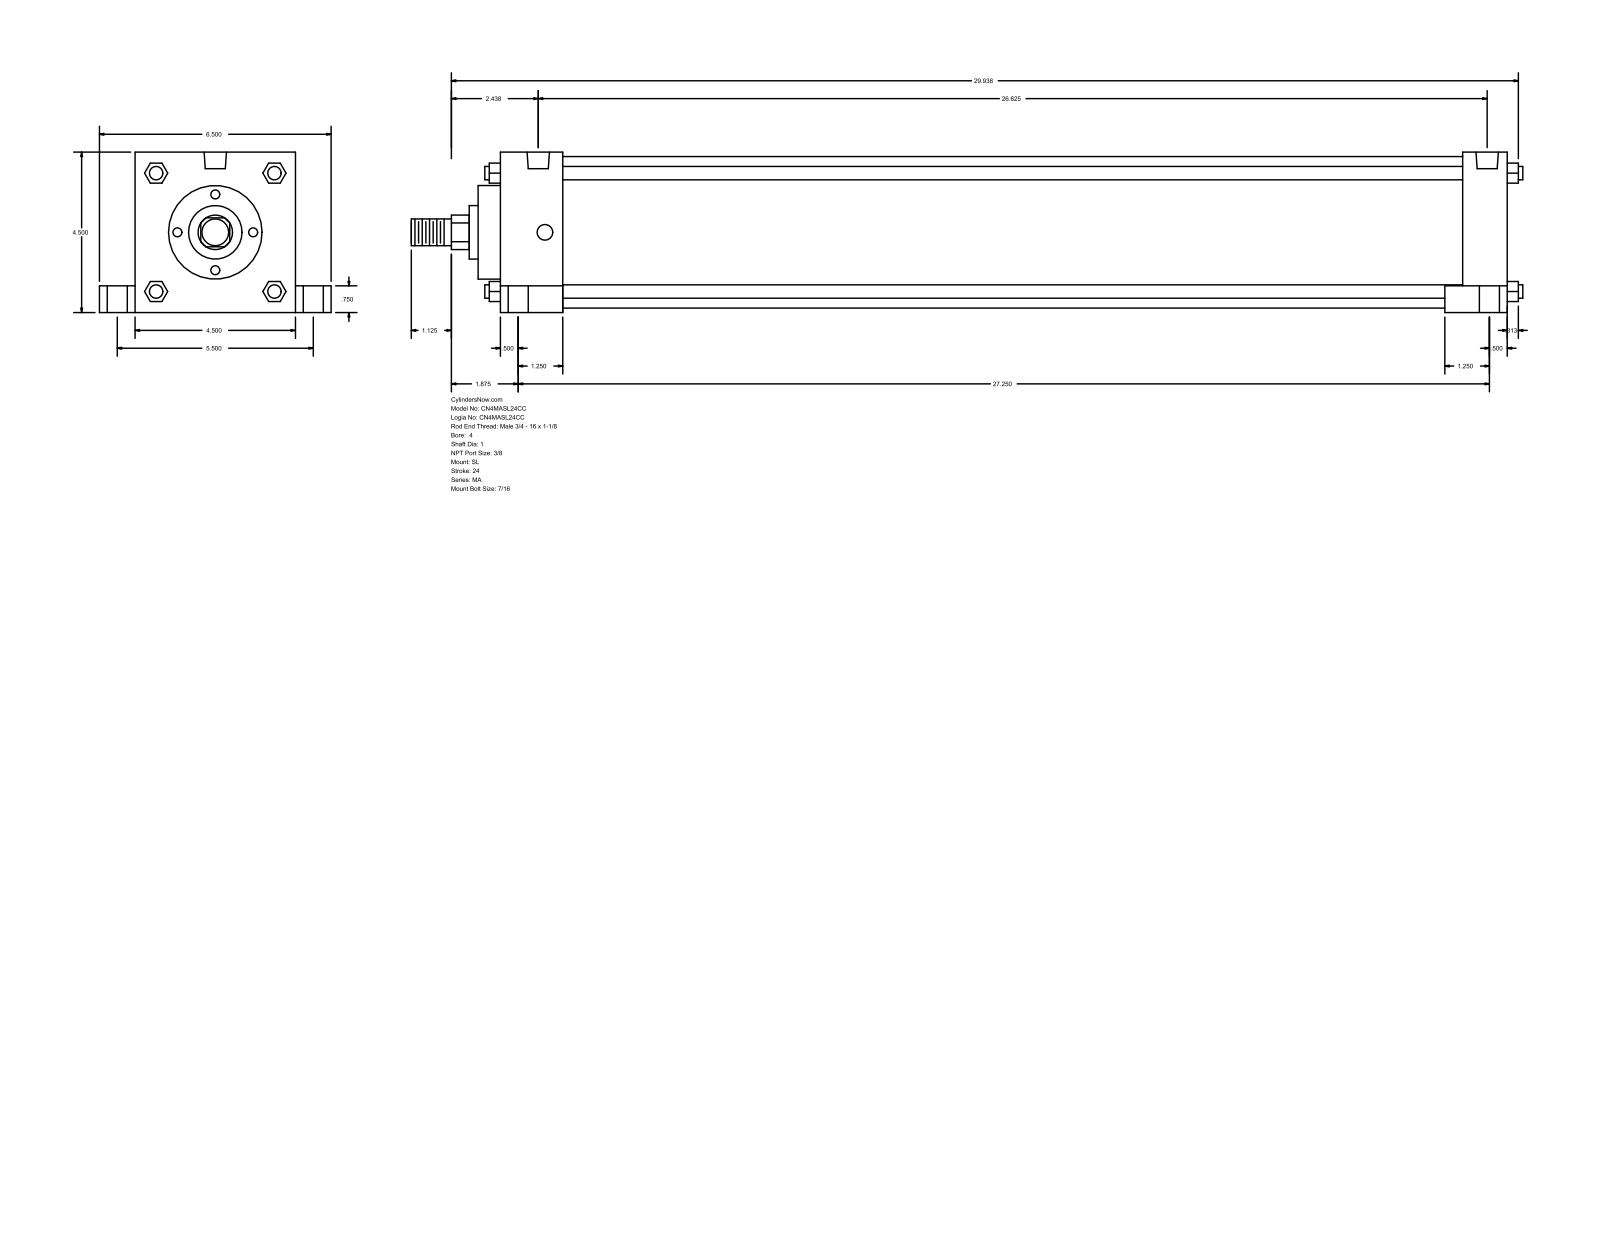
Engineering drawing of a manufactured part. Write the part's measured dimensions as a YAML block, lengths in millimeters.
part_name: "MA_SL__0400_1"
step_written_by: "GSSL Pune (CONFIG_CONTROL_DESIGN)"
units: millimeters
bodies: {solids: 0, faces: 150, planar: 113, cylindrical: 37, other: 0}
overall_size: [792.16, 165.1, 114.3]
round_holes:
  - {diameter: 11.11, count: 4}
  - {diameter: 14.29, count: 4}
  - {diameter: 20.64, count: 4}
  - {diameter: 15.93, count: 2}
round_bosses_or_shafts:
  - {diameter: 9.53, count: 4}
  - {diameter: 107.95, count: 1}
  - {diameter: 66.67, count: 1}
  - {diameter: 38.1, count: 1}
  - {diameter: 25.4, count: 1}
  - {diameter: 19.05, count: 1}
partial_cylinders:
  - {radius: 12.29, count: 1}
face_to_face_distances: [114.3, 717.56, 641.35, 44.46, 673.1, 685.81, 31.75, 25.4, 139.7, 19.05]
hole_center_spacings: [69.87, 70.14, 71.3, 72.4, 139.7, 666.75, 676.71, 681.45]
